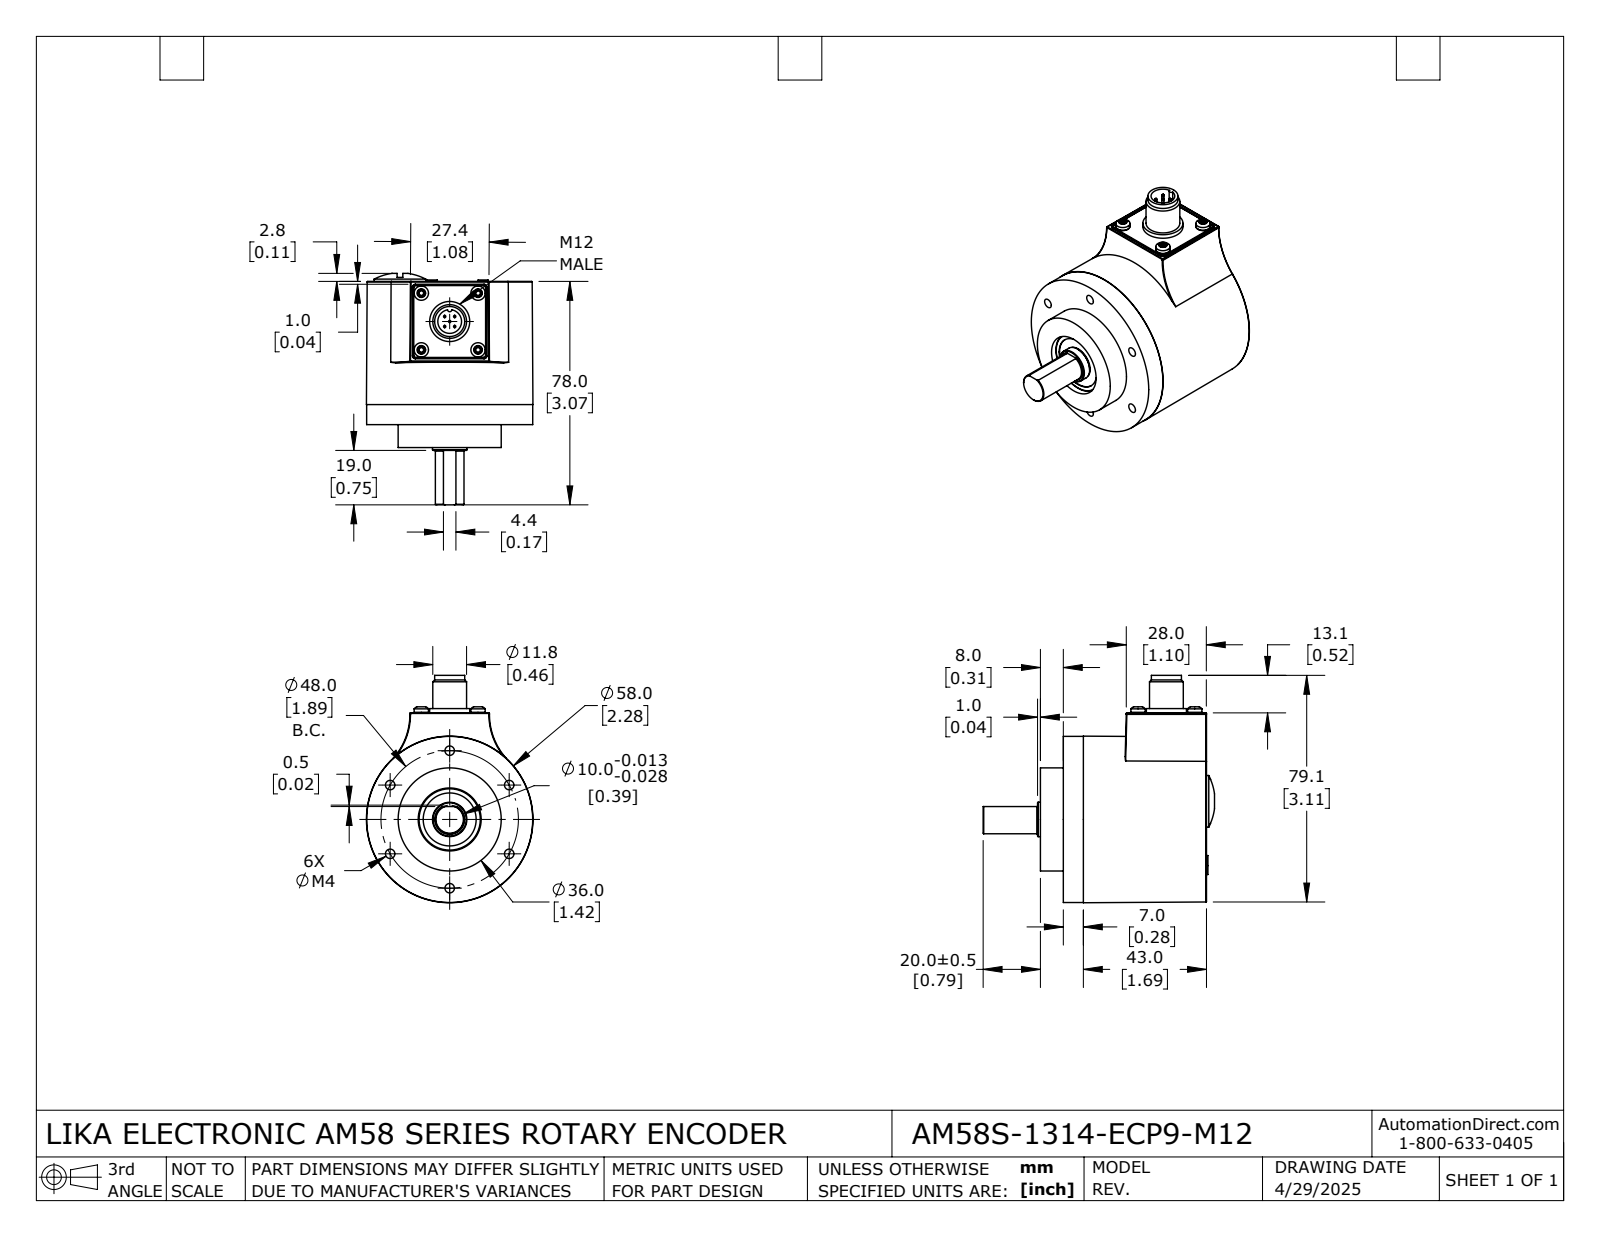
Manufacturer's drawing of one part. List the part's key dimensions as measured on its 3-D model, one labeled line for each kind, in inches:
Part name (STEP PRODUCT): AM58S-1314-ECP9-M12
STEP written by: SolidWorks 2024 (AUTOMOTIVE_DESIGN)
Units: inches
Bodies: 40 solids, 1396 faces (371 planar, 483 cylindrical, 542 other)
Overall size (bounding box): 3.406 × 2.283 × 2.283
Volume: 3.742 in³ · Surface area: 76.06 in²
Round holes (diameter × count): ⌀0.079 ×11, ⌀0.047 ×10, ⌀0.13 ×6, ⌀0.081 ×5, ⌀0.138 ×5, ⌀0.063 ×4, ⌀0.098 ×4, ⌀0.492 ×3, ⌀0.382 ×2, ⌀0.429 ×2, ⌀0.041 ×1, ⌀0.126 ×1
Round bosses / shafts (diameter × count): ⌀0.063 ×12, ⌀0.039 ×12, ⌀0.118 ×6, ⌀0.524 ×3, ⌀0.472 ×2, ⌀2.283 ×1, ⌀2.185 ×1, ⌀2.165 ×1
Partial cylindrical surfaces — rounded edges, fillets, slot ends (radius × count): R0.008 ×26, R0.039 ×25, R0.118 ×3, R0.269 ×3, R0.299 ×3, R0.317 ×3, R0.354 ×3, R0.392 ×3
Main face-to-face distances: 0.098, 0.394, 1.594, 0.079, 1.693, 0.276, 0.197, 0.039, 0.118, 0.315
Hole centre spacings: 0.098, 0.139, 1.334, 0.197, 0.209, 0.295, 0.669, 0.791
